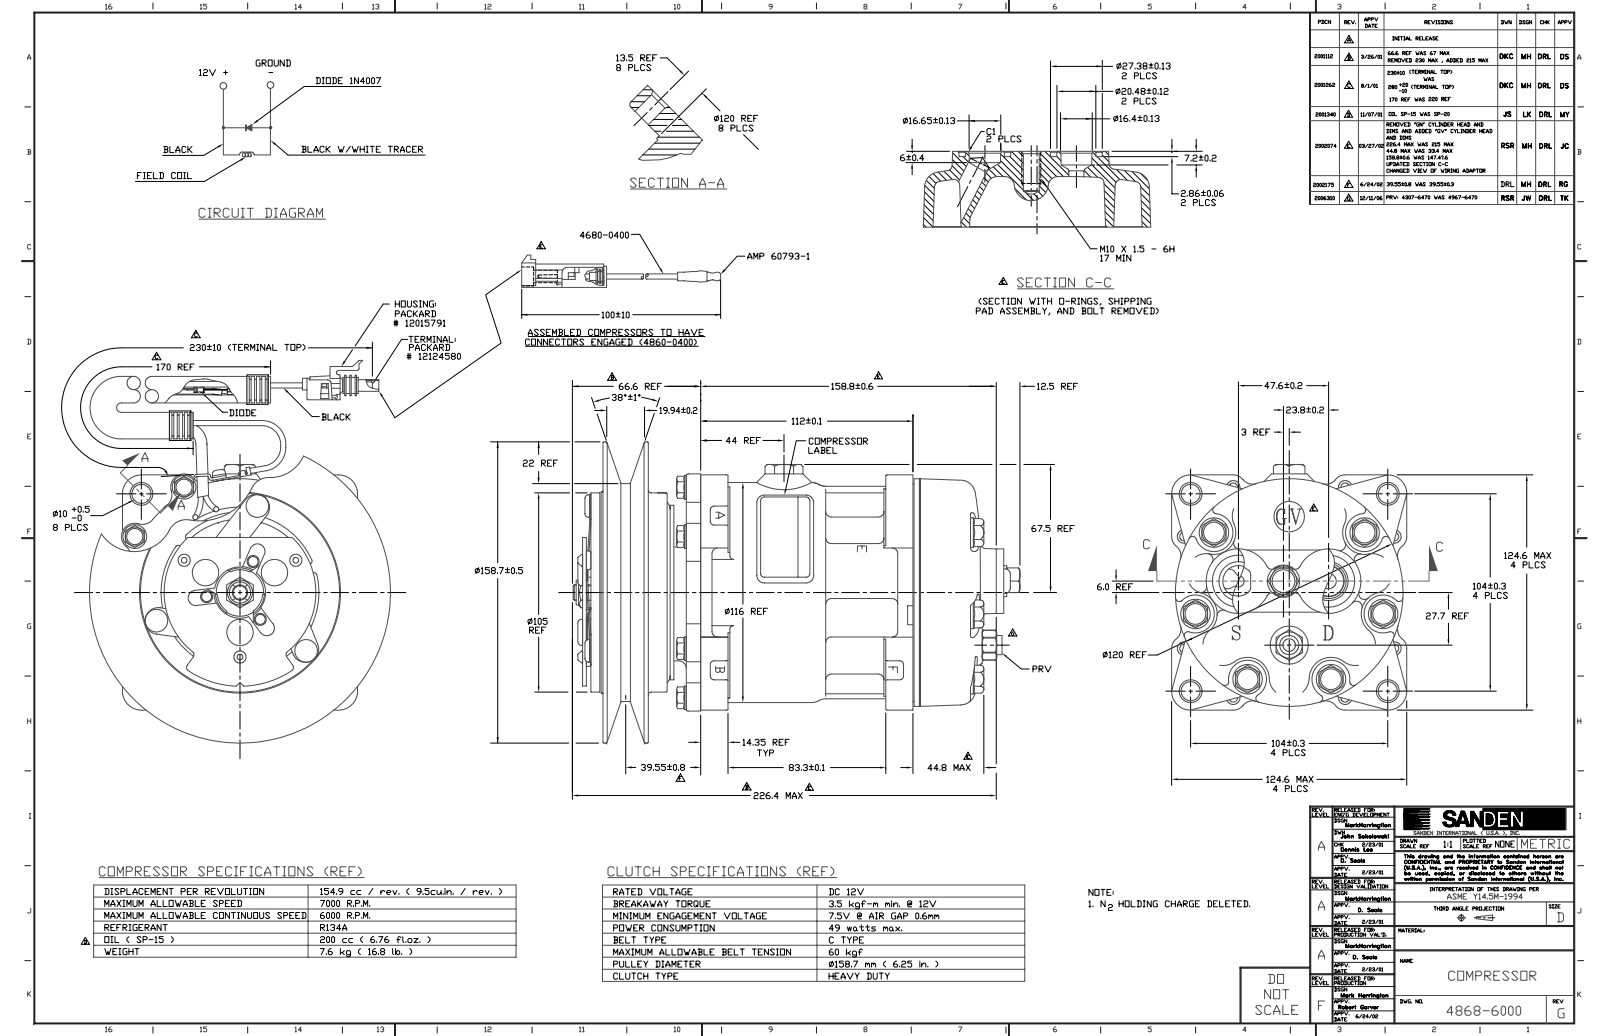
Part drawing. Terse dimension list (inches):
name: SANDEN_4868_REV_G_COMPR_AC1
written by: SolidWorks 2010 (CONFIG_CONTROL_DESIGN)
unit: in
bodies: 3 solids, 2577 faces (722 planar, 715 cylindrical, 1140 other)
size: 18.275 × 8.887 × 6.248
volume: 138.3 in³; area: 425.5 in²
holes: 9× ⌀0.335, 8× ⌀0.217, 8× ⌀0.276, 6× ⌀0.469, 4× ⌀0.315, 4× ⌀0.404, 3× ⌀0.087, 3× ⌀0.2, 3× ⌀0.26, 2× ⌀1.078, 1× ⌀0.043, 1× ⌀0.138
bosses: 8× ⌀0.508, 8× ⌀0.224, 6× ⌀0.602, 6× ⌀0.106, 3× ⌀0.551, 3× ⌀0.472, 3× ⌀0.394, 3× ⌀0.311
rounds: 33× R0.276, 31× R0.079, 26× R0.039, 25× R0.256, 24× R0.118, 19× R0.197, 13× R0.157, 12× R0.059
face distances: 1.832, 1.729, 0.079, 0.26, 0.291, 1.769, 0.04, 0.63, 0.551, 0.261
hole spacings: 0.896, 1.999, 2.474, 2.895, 3.212, 4.094, 4.324, 5.311
